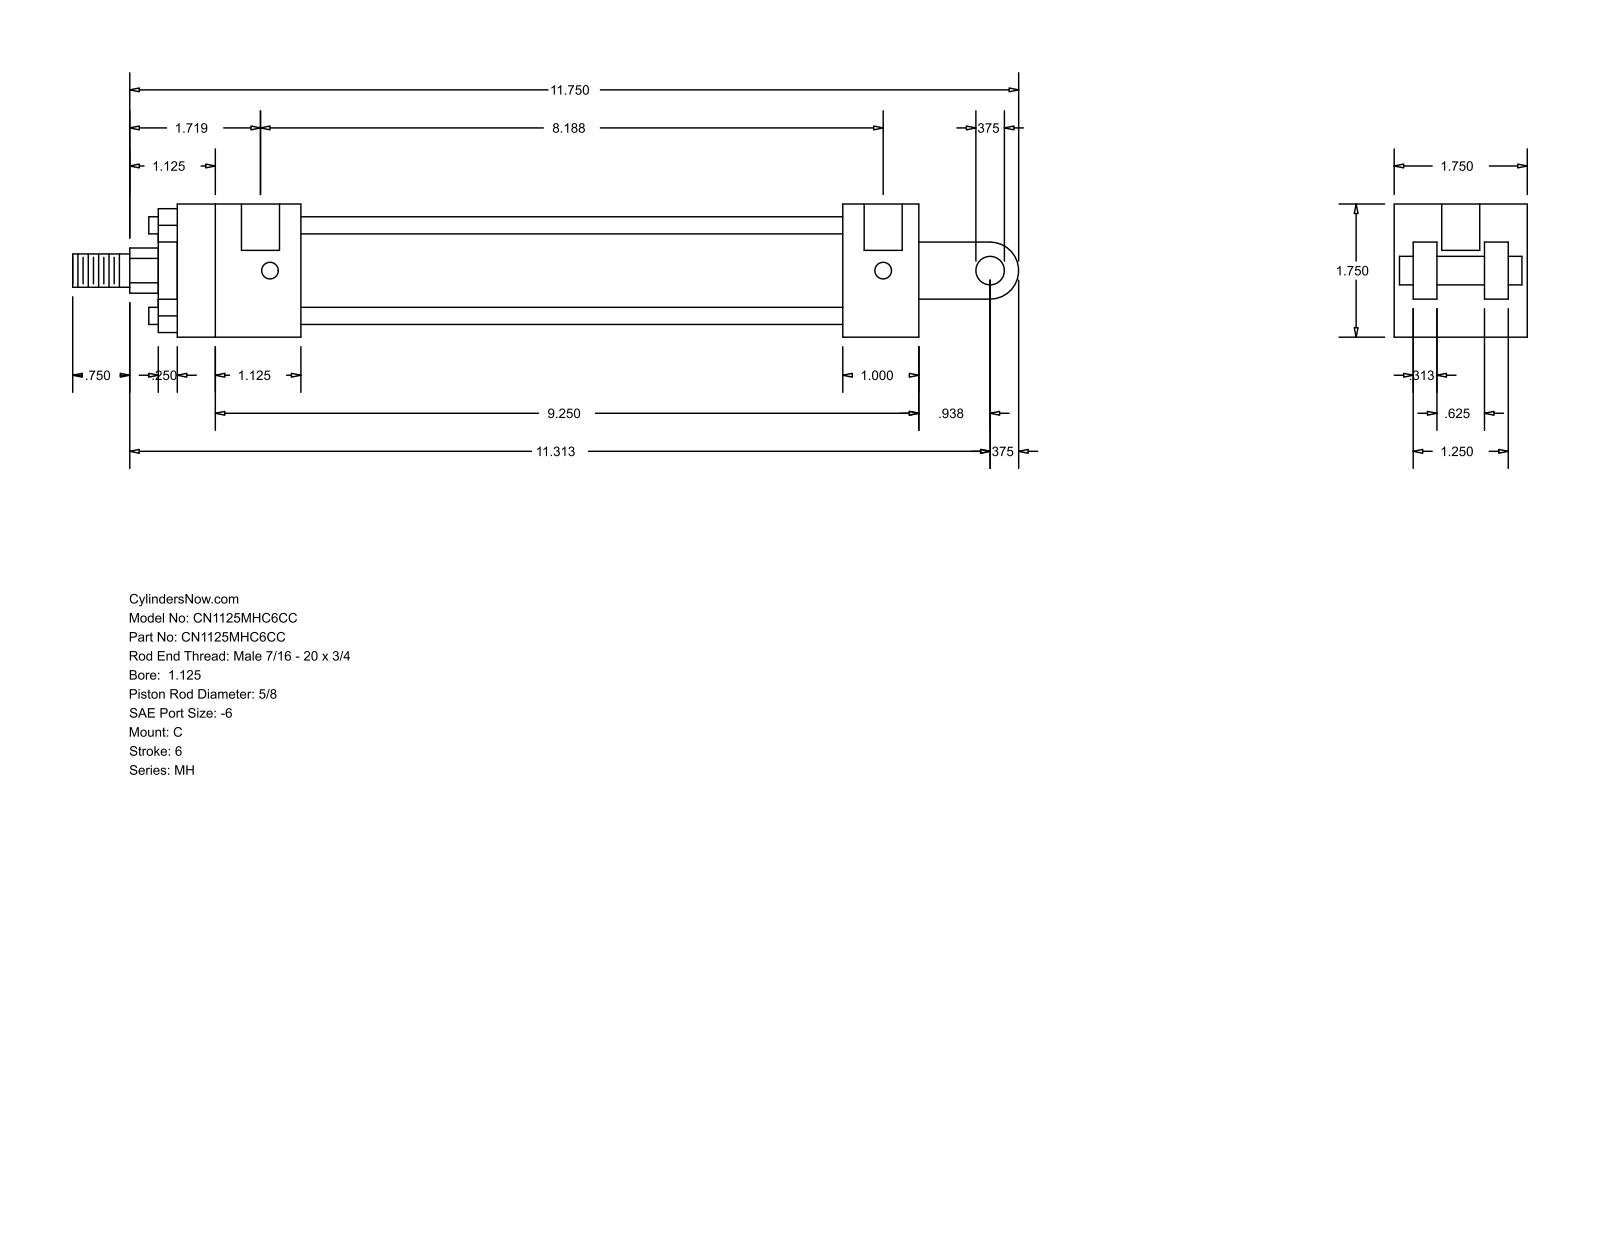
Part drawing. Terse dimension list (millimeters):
name: MH_C__0112_0.625
written by: GSSL Pune (CONFIG_CONTROL_DESIGN)
unit: mm
bodies: 0 solids, 99 faces (70 planar, 29 cylindrical, 0 other)
size: 315.91 × 44.45 × 44.45
holes: 4× ⌀5.56, 2× ⌀12.7
bosses: 4× ⌀5.71, 1× ⌀34.92, 1× ⌀28.57, 1× ⌀15.88, 1× ⌀11.11, 1× ⌀9.53
rounds: 1× R7.54, 1× R9.53
face distances: 44.46, 6.35, 31.76, 14.29, 25.4, 30.17, 38.11, 7.94, 23.82, 12.7
hole spacings: 204.79, 3.17, 207.96
